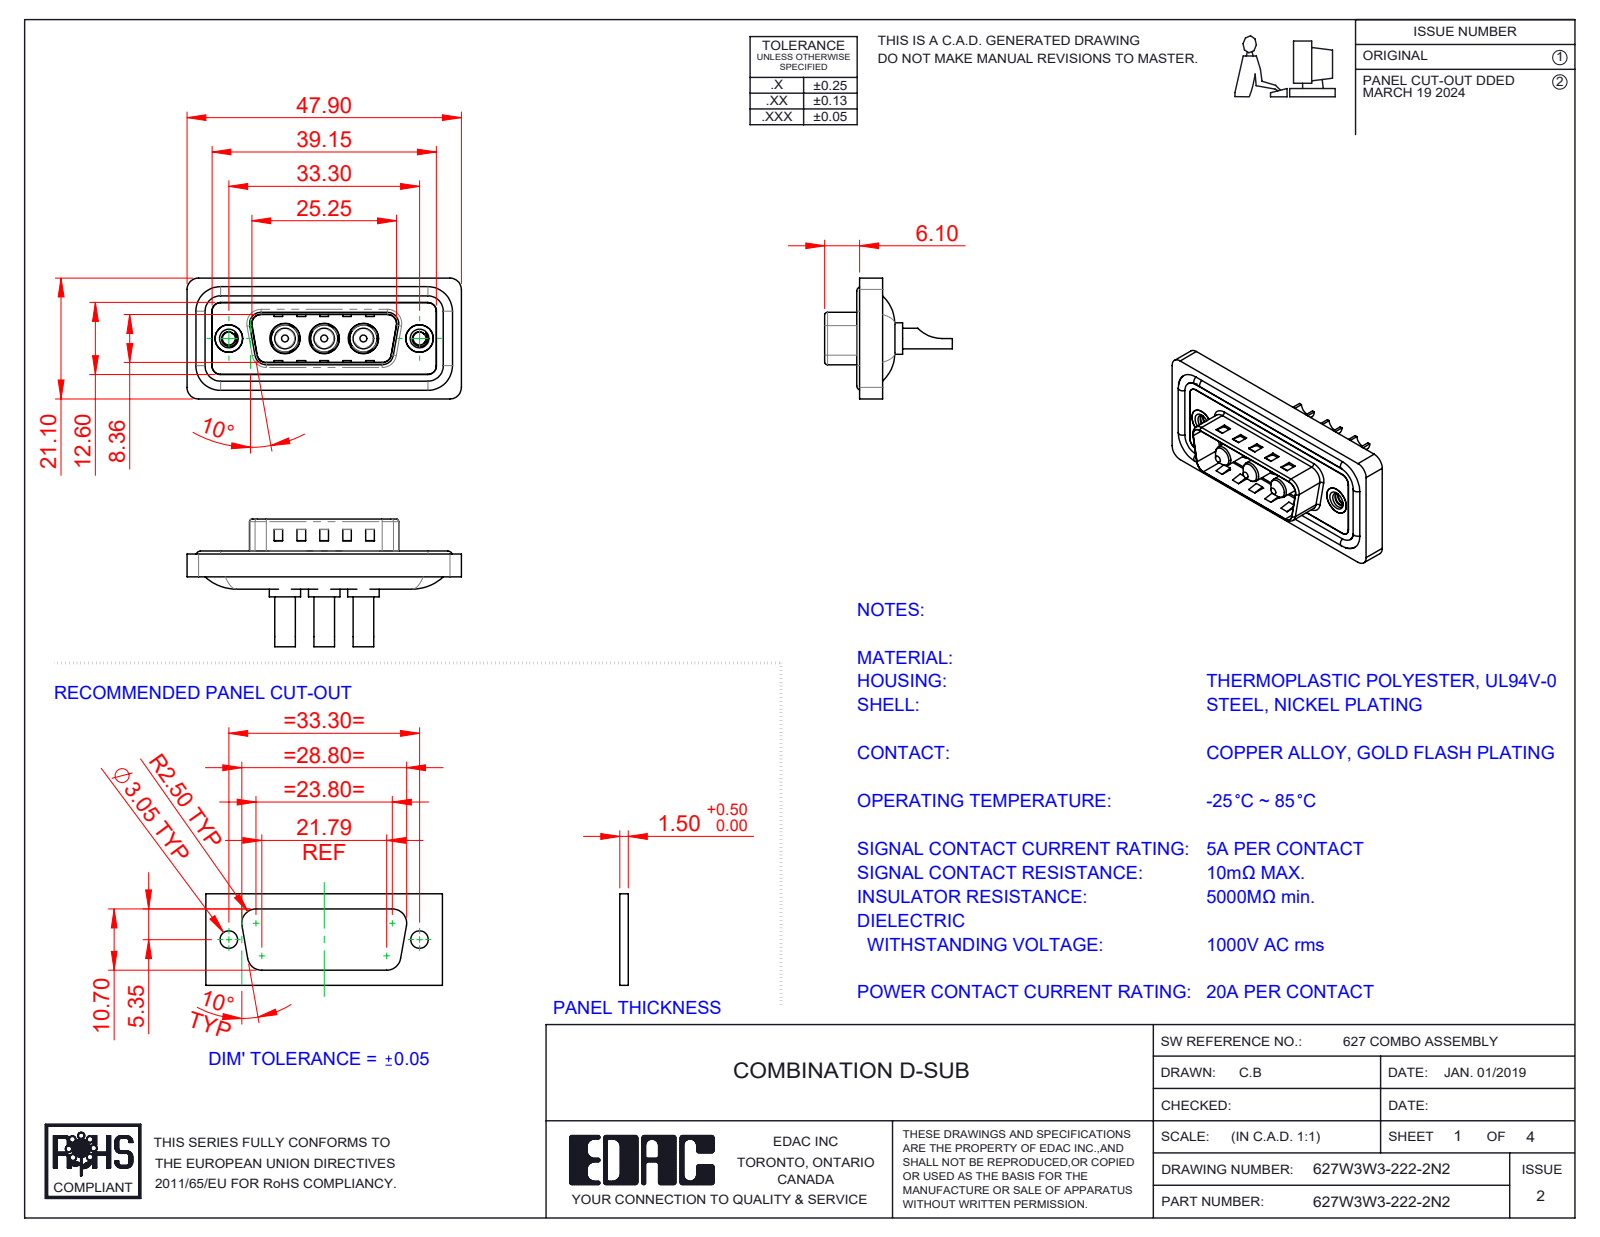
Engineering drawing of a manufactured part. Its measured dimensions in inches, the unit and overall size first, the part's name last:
Units: inches
Overall size (bounding box): 1.886 × 0.878 × 0.831
Round holes (diameter × count): ⌀0.106 ×3, ⌀0.191 ×3, ⌀0.209 ×3, ⌀0.089 ×2, ⌀0.157 ×2, ⌀0.189 ×2, ⌀0.197 ×2
Round bosses / shafts (diameter × count): ⌀0.063 ×4, ⌀0.217 ×3, ⌀0.205 ×3, ⌀0.187 ×3, ⌀0.148 ×3, ⌀0.142 ×3, ⌀0.193 ×2
Partial cylindrical surfaces — rounded edges, fillets, slot ends (radius × count): R0.059 ×26, R0.079 ×20, R0.02 ×8, R0.063 ×8, R0.01 ×4, R0.024 ×4, R0.026 ×4, R0.035 ×4
Main face-to-face distances: 0.016, 0.043, 0.059, 0.02, 0.063, 0.122, 0.114, 0.157, 0.032, 0.377
Hole centre spacings: 0.27, 0.386, 0.656, 0.925, 0.539, 1.311
Volume: 0.343 in³ · Surface area: 13.95 in²
Bodies: 13 solids, 585 faces (216 planar, 250 cylindrical, 119 other)
Part name (STEP PRODUCT): 627Combo Shell Front_15 Contacts; 627W3W3-222-2N2; Power Pin_20A SC; 627Combo Housing_3W3 (+3 more)
STEP written by: SolidWorks 2023 (CONFIG_CONTROL_DESIGN)
